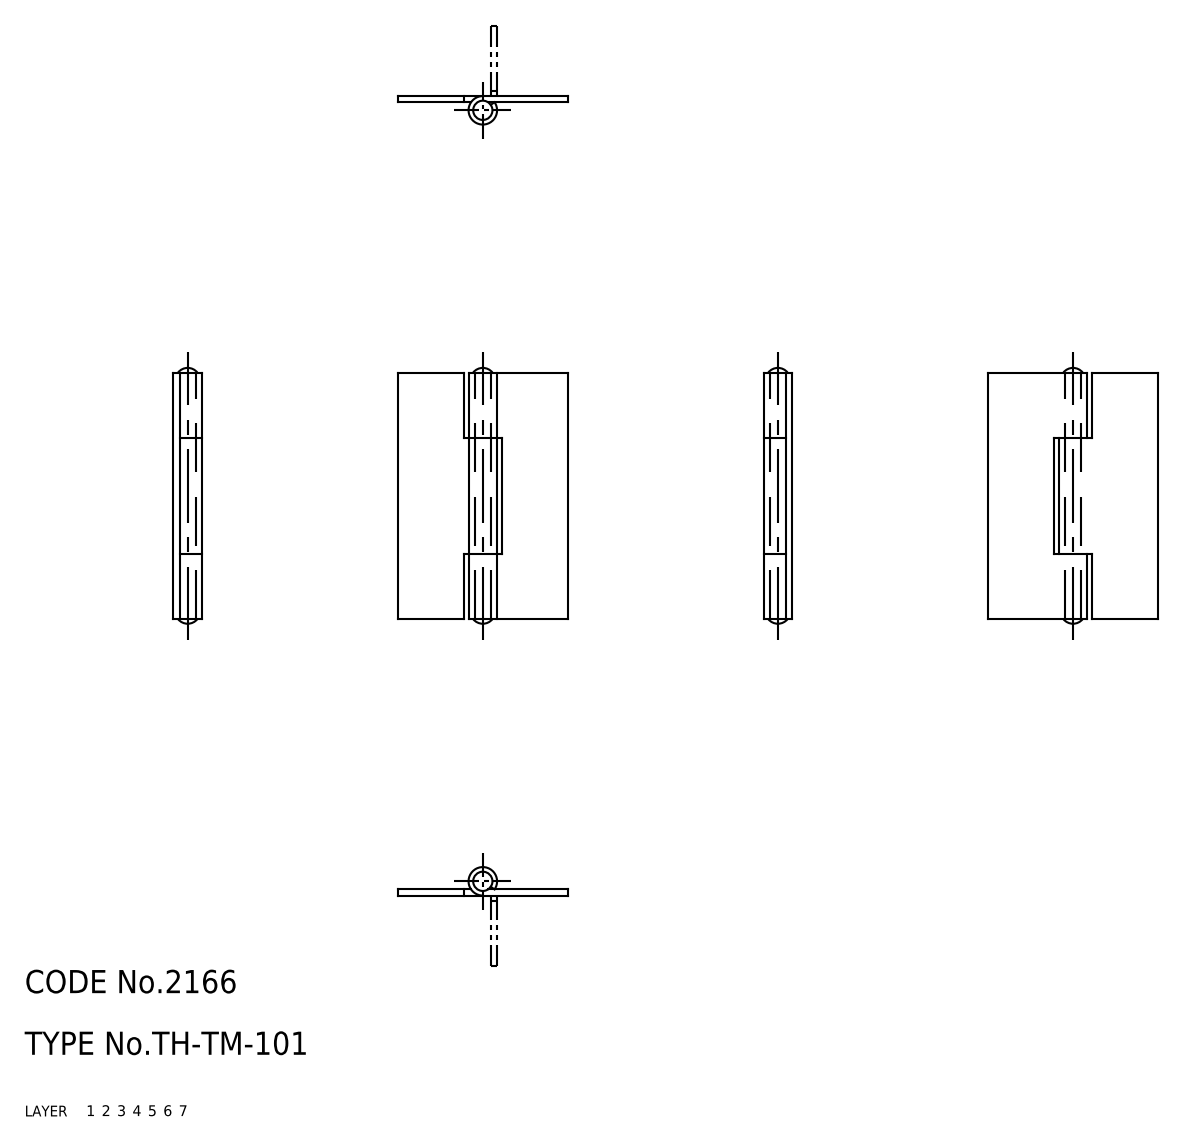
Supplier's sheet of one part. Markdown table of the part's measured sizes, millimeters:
| quantity | value |
| --- | --- |
| part name | 67110385; 67110398; 67110411 |
| STEP written by | CADfix (AUTOMOTIVE_DESIGN) |
| units | millimeters |
| bodies | 3 solids, 32 faces (0 planar, 0 cylindrical, 32 other) |
| overall size | 33.2 × 22 × 3.7 |
| volume | 810 mm³ |
| surface area | 2 143 mm² |
